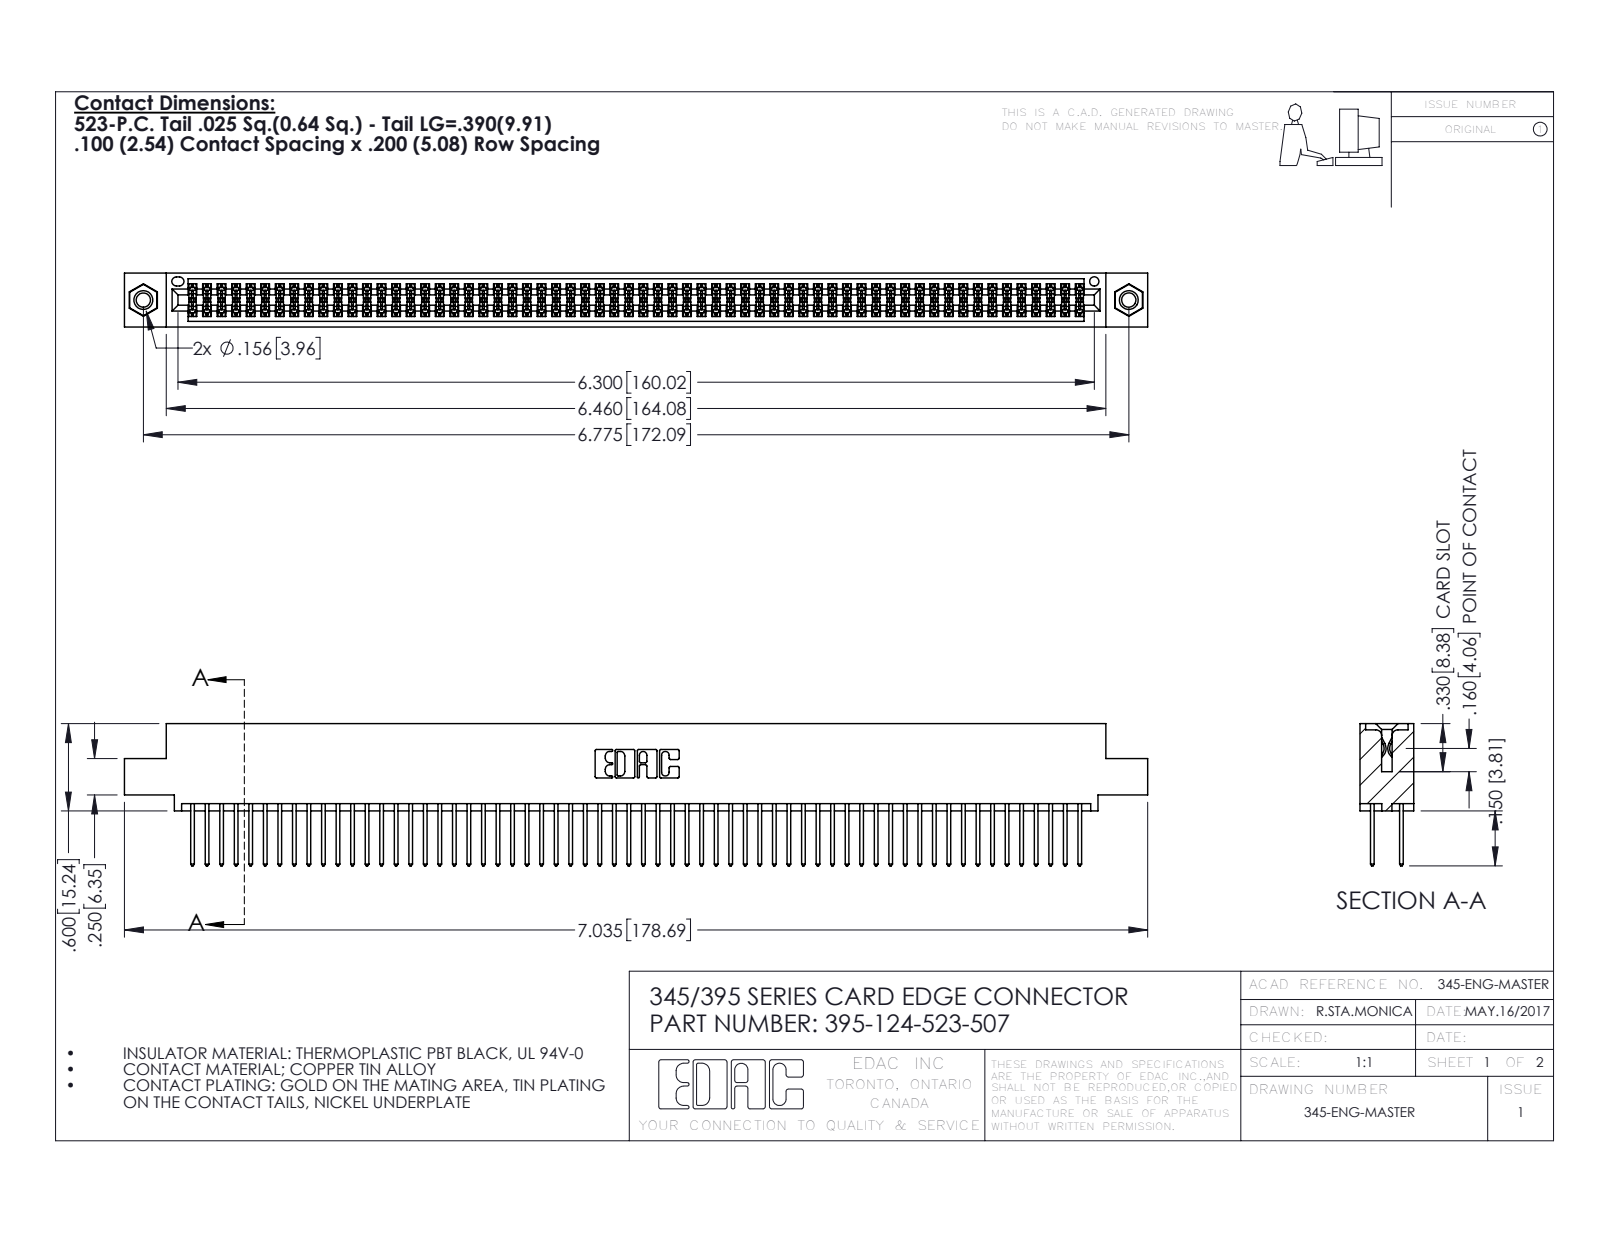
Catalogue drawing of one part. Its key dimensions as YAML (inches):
part_name: "395-124-523-507; 345-292-001_345-293-123; 345-250-001_345-250-005-103; 345 Part_0.110 Offset - 0.156 Dia-TI"
step_written_by: "SolidWorks 2016 (CONFIG_CONTROL_DESIGN)"
units: inches
bodies: {solids: 127, faces: 6390, planar: 4208, cylindrical: 2166, other: 16}
overall_size: [7.035, 0.977, 0.37]
volume: 1.081
surface_area: 43.13
round_holes:
  - {diameter: 0.098, count: 2}
  - {diameter: 0.125, count: 2}
  - {diameter: 0.156, count: 2}
  - {diameter: 0.064, count: 1}
round_bosses_or_shafts:
  - {diameter: 0.155, count: 2}
partial_cylinders:
  - {radius: 0.006, count: 186}
  - {radius: 0.01, count: 124}
  - {radius: 0.01, count: 22}
  - {radius: 0.007, count: 6}
  - {radius: 0.031, count: 6}
  - {radius: 0.026, count: 3}
  - {radius: 0.014, count: 2}
  - {radius: 0.019, count: 2}
face_to_face_distances: [0.072, 0.298, 0.2, 0.098, 0.272, 0.025, 0.37, 0.225, 0.175, 0.149]
hole_center_spacings: [0.27, 6.539, 6.775]
